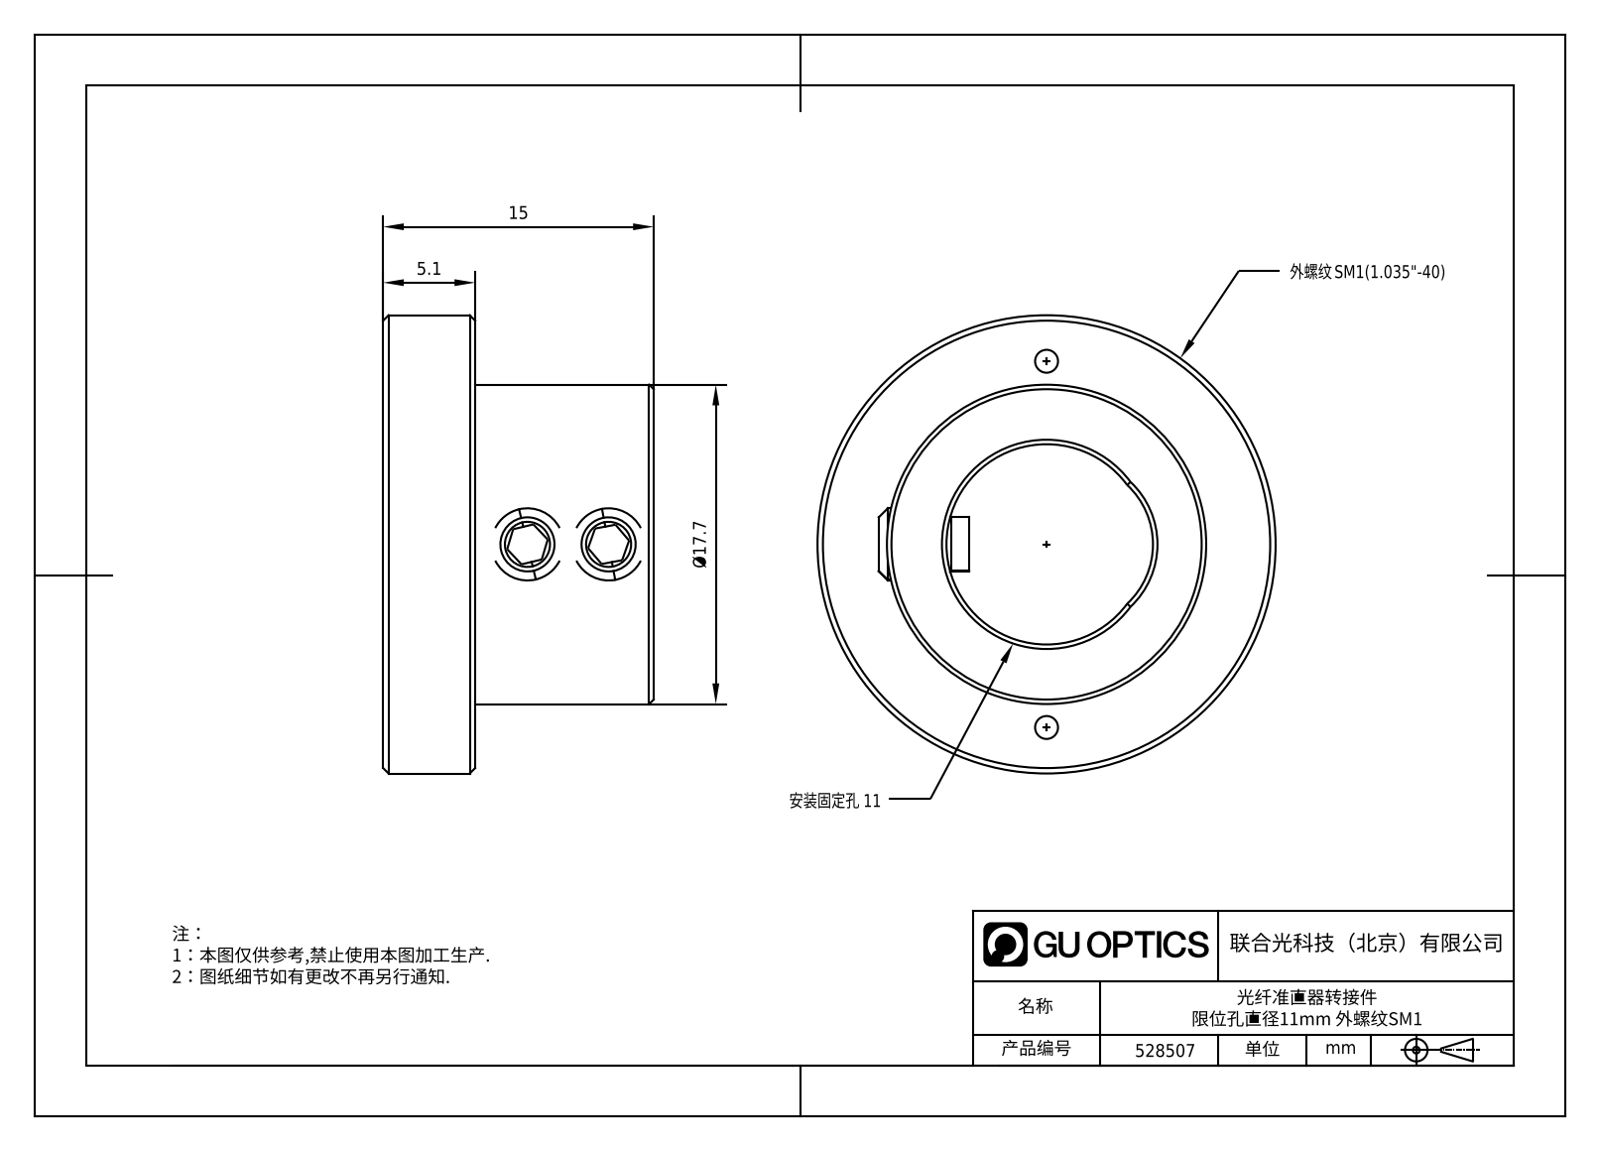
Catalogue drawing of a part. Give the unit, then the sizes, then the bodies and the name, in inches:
Units: inches
Overall size (bounding box): 1 × 1 × 0.591
Round holes (diameter × count): ⌀0.05 ×2, ⌀0.13 ×2, ⌀0.437 ×1
Round bosses / shafts (diameter × count): ⌀0.157 ×2, ⌀0.118 ×2, ⌀1 ×1, ⌀0.697 ×1
Partial cylindrical surfaces — rounded edges, fillets, slot ends (radius × count): R0.177 ×1
Main face-to-face distances: 0.201, 0.591, 0.39, 0.157, 0.079, 0.05, 0.151, 0.197, 0.039, 0.101
Hole centre spacings: 0.4, 0.177, 0.799
Volume: 0.218 in³ · Surface area: 3.833 in²
Bodies: 3 solids, 83 faces (25 planar, 28 cylindrical, 30 other)
STEP written by: SolidWorks 2021 (CONFIG_CONTROL_DESIGN)
